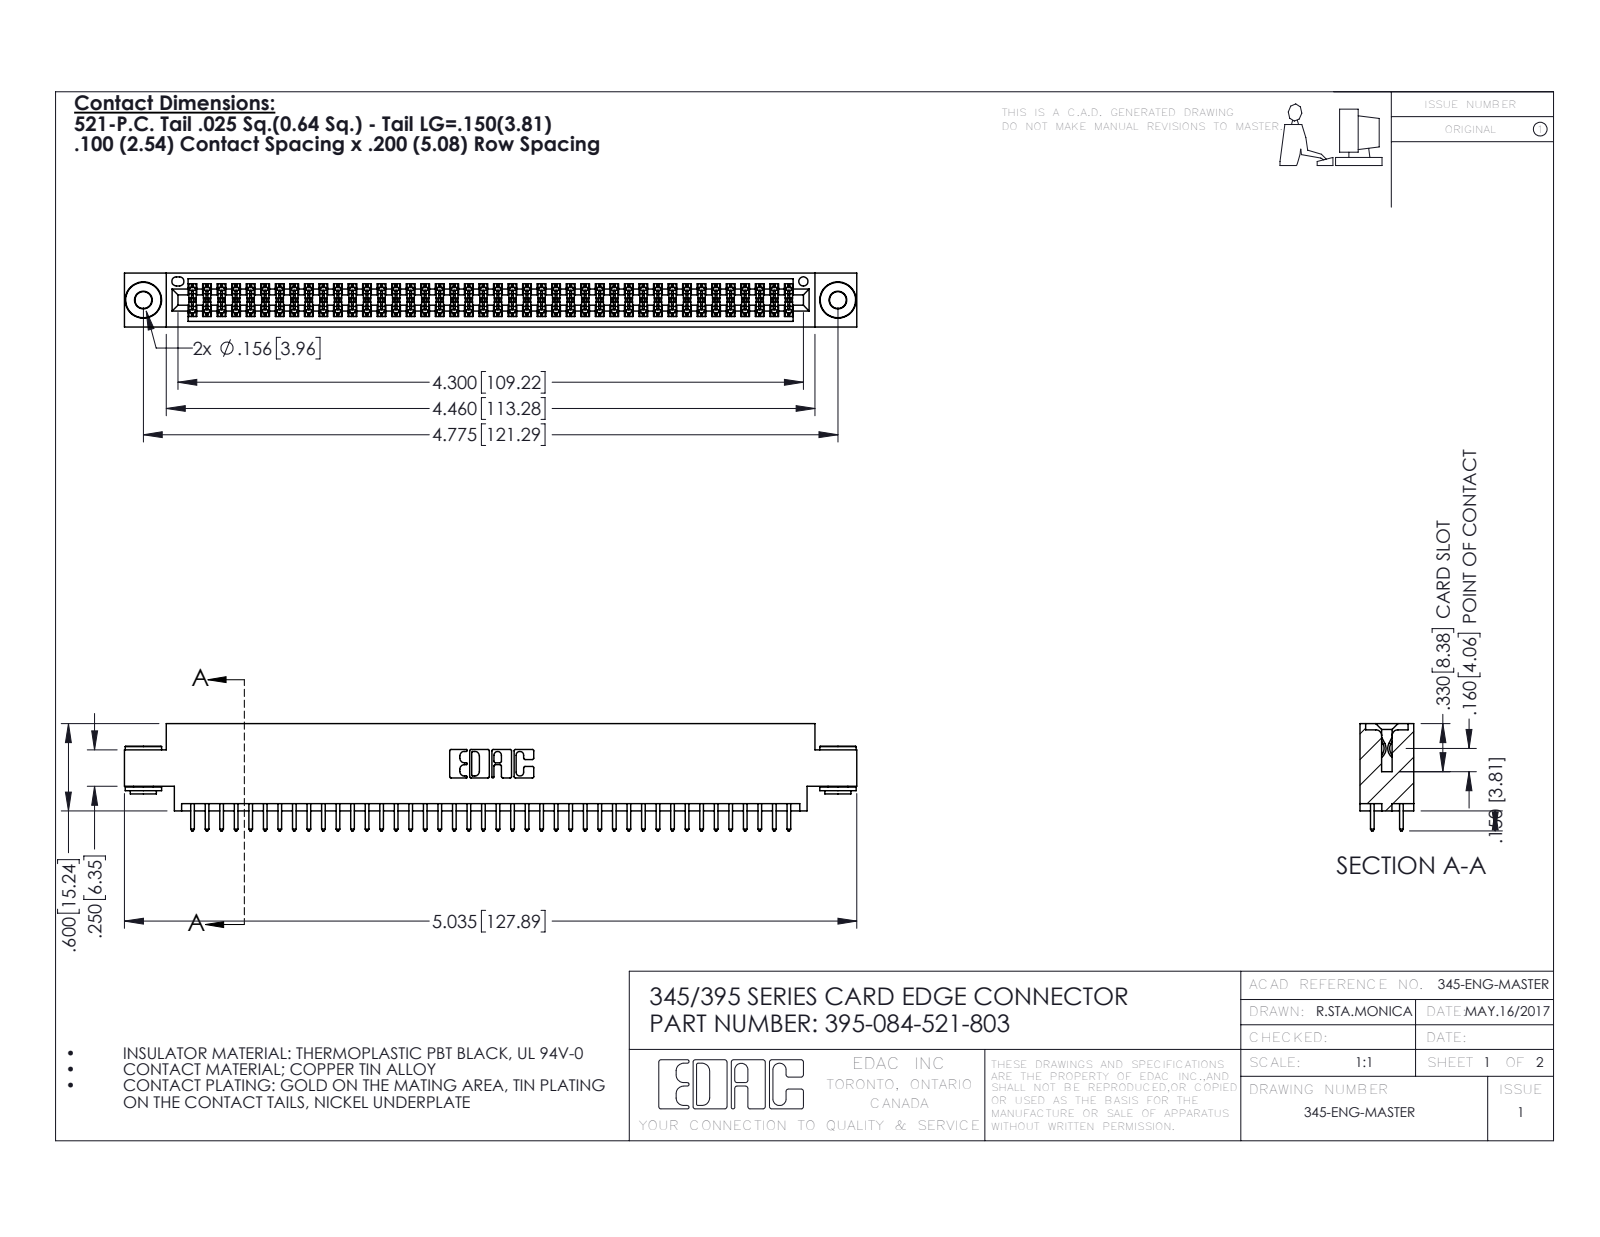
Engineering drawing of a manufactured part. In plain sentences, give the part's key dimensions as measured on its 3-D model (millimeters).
The part is named "345 Part_0.170 Offset - 0.156 Dia-TH; 395-084-521-803; 345-292-001_345-293-121; 345-250-002_345-250-002-102". Its 3-D file was written by "SolidWorks 2016 (CONFIG_CONTROL_DESIGN)". It is 87 solids with 4368 faces: 2866 planar, 1494 cylindrical and 8 other. Overall it measures 127.9 by 18.7 by 9.4 millimeters. Its volume is 12 300 cubic millimeters and its surface area 18 300 square millimeters. Round holes: 2 of diameter 2.9, 2 of diameter 4, 1 of diameter 1.6. Round bosses or shafts: 2 of diameter 6.4, 2 of diameter 4.6, 2 of diameter 3.5. Partial cylindrical surfaces (rounded edges, fillets, slot ends): 126 of radius 0.2, 84 of radius 0.3, 22 of radius 0.3, 6 of radius 0.2, 6 of radius 0.8, 3 of radius 0.7, 2 of radius 0.4, 2 of radius 0.5. The main face-to-face distances are 1.8, 7.6, 5.1, 9.4, 2.5, 6.9, 0.6, 5.7, 4.4, 3.8. The hole center spacings are 6.9, 115.3, 121.3.
